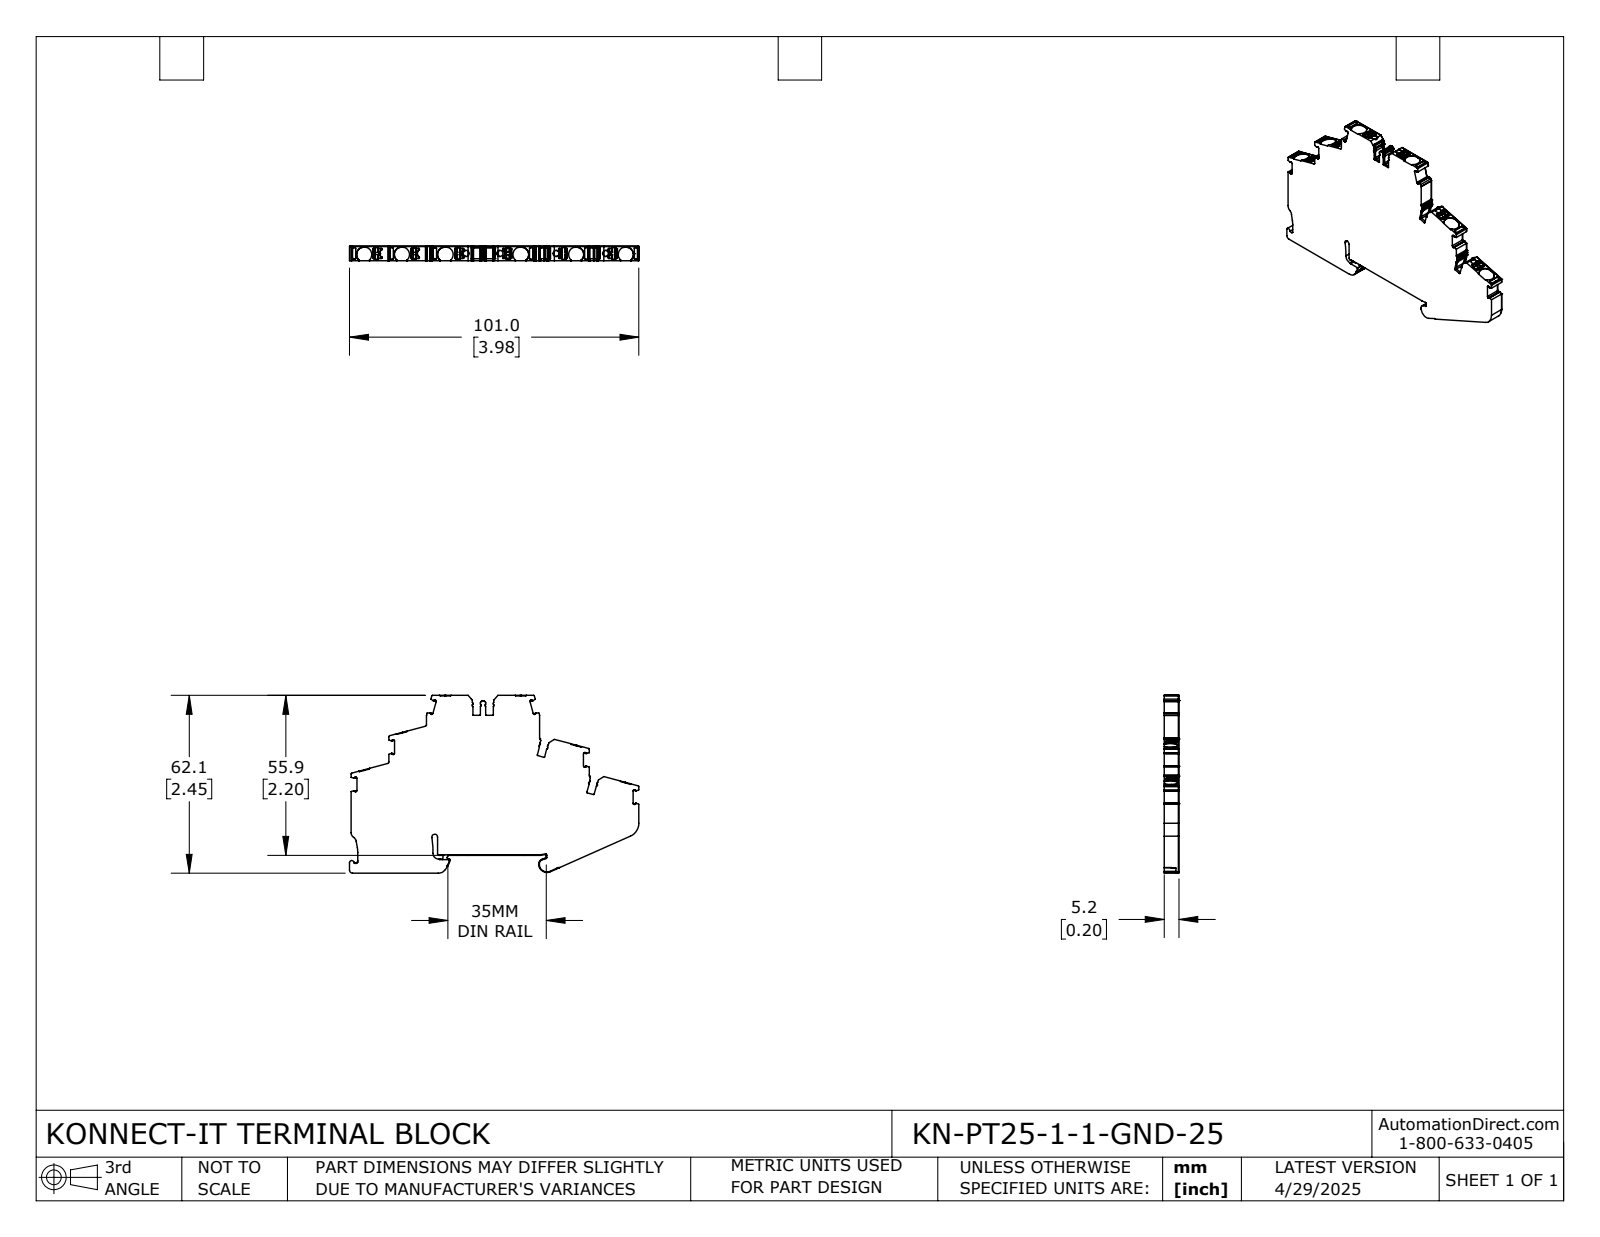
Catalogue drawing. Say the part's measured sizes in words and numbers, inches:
The part is named "KN-PT25-1-1-GND-25". Its 3-D file was written by "SolidWorks 2024 (CONFIG_CONTROL_DESIGN)". It is 8 solids with 1470 faces: 670 planar, 651 cylindrical and 149 other. Overall it measures 3.977 by 2.445 by 0.203 inches. Its volume is 1.393 cubic inches and its surface area 19.17 square inches. Round holes: 4 of diameter 0.083. Partial cylindrical surfaces (rounded edges, fillets, slot ends): 137 of radius 0.008, 55 of radius 0.004, 53 of radius 0.012, 39 of radius 0.02, 36 of radius 0.006, 25 of radius 0.016, 16 of radius 0.039, 14 of radius 0.024. The main face-to-face distances are 0.203, 0.053, 0.1, 0.102, 0.15, 0.047, 2.191, 0.246, 0.079, 0.035. The hole center spacings are 0.466, 0.792.
